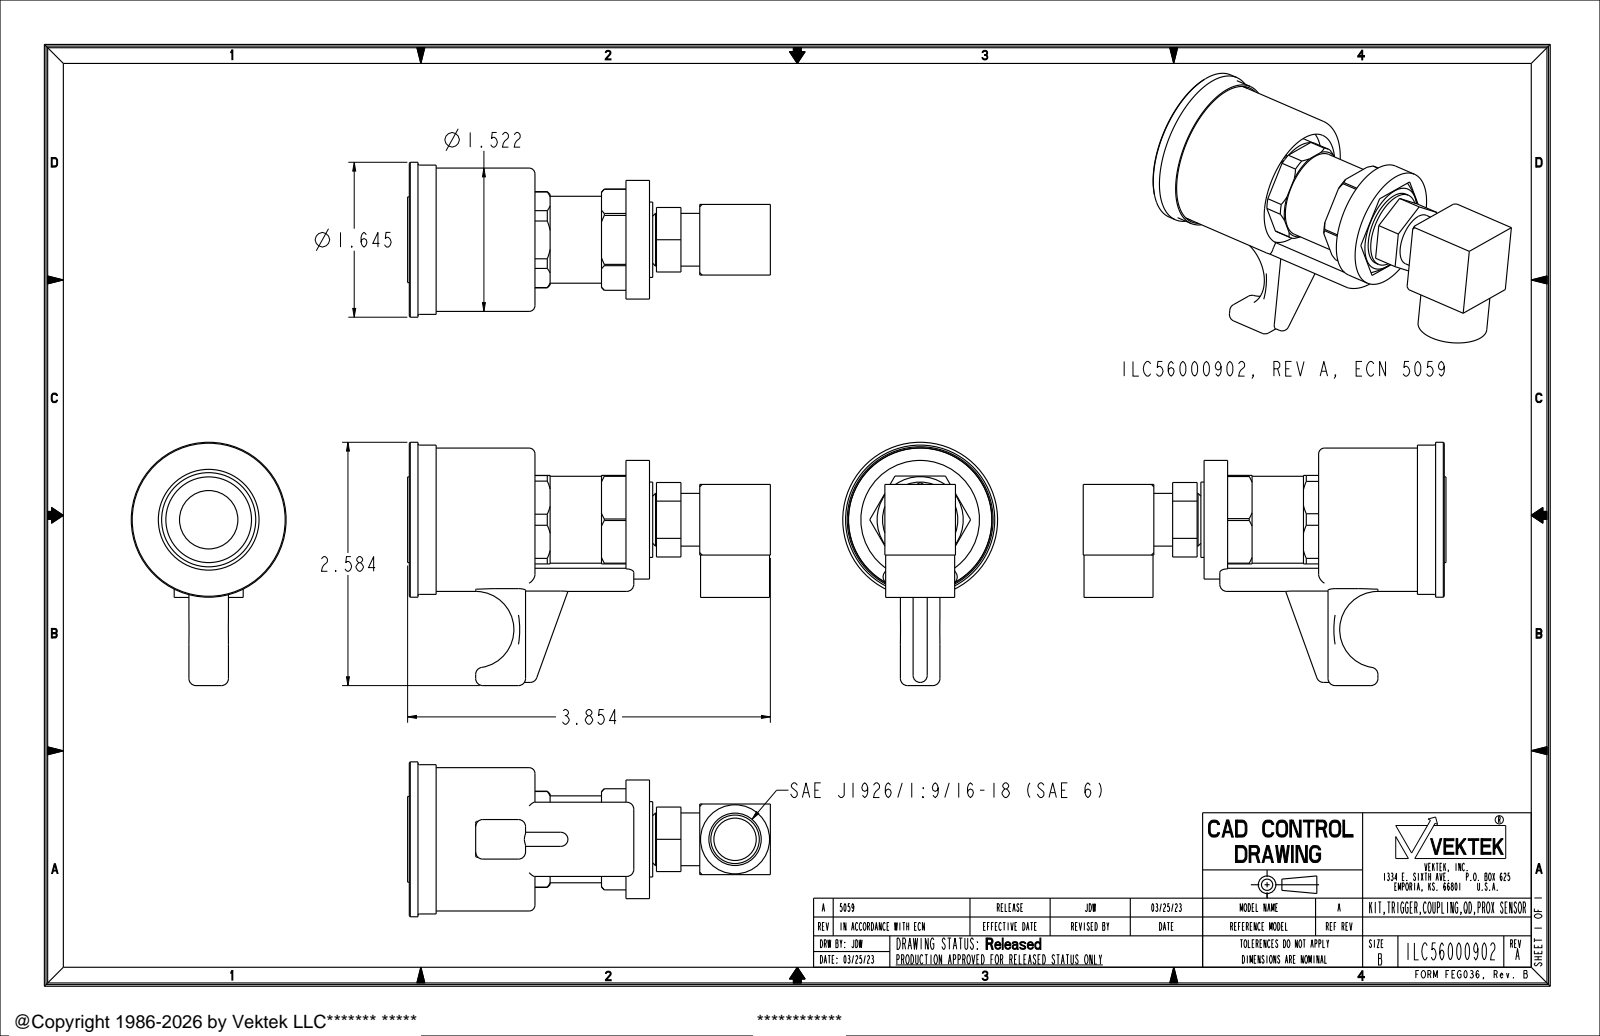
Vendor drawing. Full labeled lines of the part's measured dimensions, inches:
Part name (STEP PRODUCT): ILC56000902
STEP written by: CREO PARAMETRIC BY PTC INC, 2021164 (AUTOMOTIVE_DESIGN)
Units: inches
Bodies: 1 solid, 222 faces (94 planar, 75 cylindrical, 53 other)
Overall size (bounding box): 3.854 × 2.425 × 1.857
Volume: 3.82 in³ · Surface area: 39.34 in²
Round holes (diameter × count): ⌀0.094 ×1, ⌀0.22 ×1, ⌀0.3 ×1, ⌀0.45 ×1, ⌀0.509 ×1, ⌀0.515 ×1, ⌀0.62 ×1, ⌀1.07 ×1, ⌀1.243 ×1, ⌀1.525 ×1
Round bosses / shafts (diameter × count): ⌀1.645 ×1, ⌀1.585 ×1, ⌀1.522 ×1, ⌀1.26 ×1, ⌀1.195 ×1, ⌀0.923 ×1, ⌀0.91 ×1, ⌀0.8 ×1
Partial cylindrical surfaces — rounded edges, fillets, slot ends (radius × count): R0.075 ×14, R0.074 ×2, R0.01 ×1, R0.059 ×1, R0.406 ×1, R0.507 ×1, R0.511 ×1, R0.537 ×1
Main face-to-face distances: 0.75, 2.552, 3.836, 1.284, 2.302, 0.25, 1.534, 0.5, 0.018, 2.32
